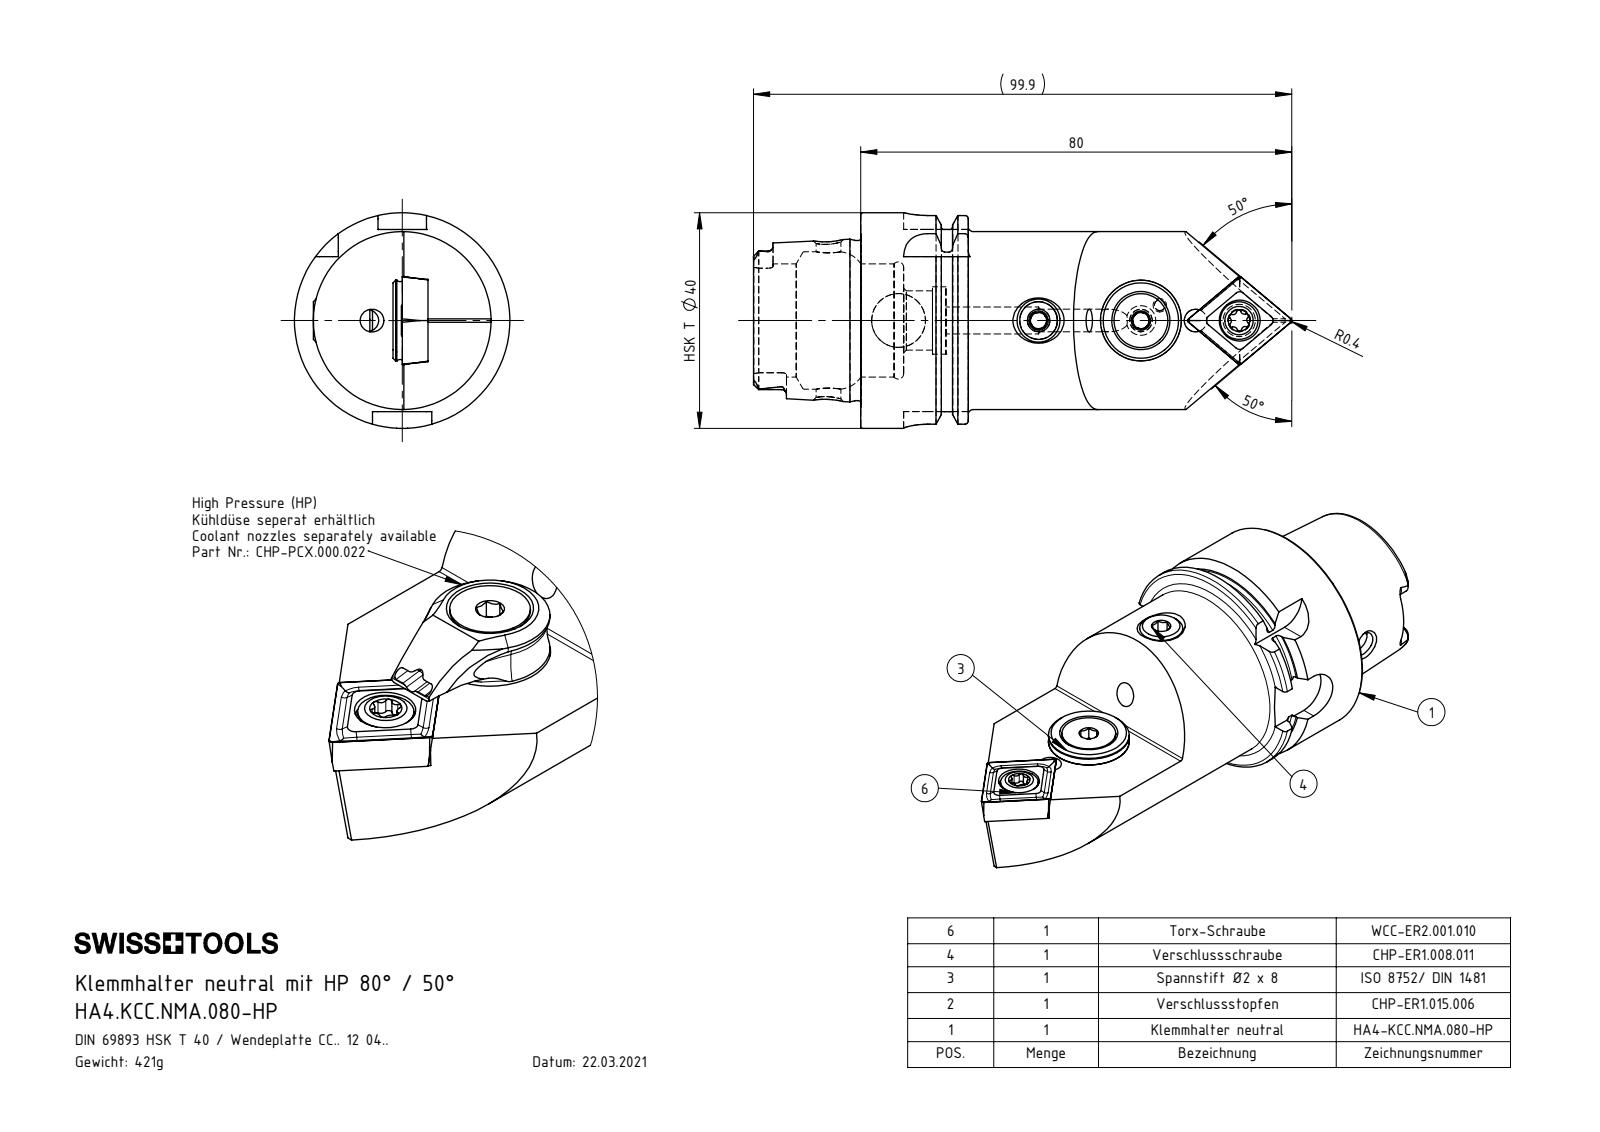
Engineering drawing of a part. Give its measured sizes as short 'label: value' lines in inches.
name: CHP-ER1.015.006; HA4-KCC.NMA.080-HP_A_Fertigbearbeitung; DIN 3771 - 13x1; CHP-ER1.015.006_A (+6 more)
written by: SolidWorks 2022 (AUTOMOTIVE_DESIGN)
unit: in
bodies: 8 solids, 396 faces (111 planar, 117 cylindrical, 168 other)
size: 3.933 × 1.575 × 1.575
volume: 3.297 in³; area: 27.84 in²
holes: 5× ⌀0.165, 1× ⌀0.047, 1× ⌀0.079, 1× ⌀0.098, 1× ⌀0.118, 1× ⌀0.181, 1× ⌀0.197, 1× ⌀0.205, 1× ⌀0.217, 1× ⌀0.276, 1× ⌀0.299, 1× ⌀0.394
bosses: 2× ⌀0.197, 1× ⌀1.575, 1× ⌀1.368, 1× ⌀1.299, 1× ⌀1.17, 1× ⌀0.591, 1× ⌀0.528, 1× ⌀0.394
rounds: 6× R0.015, 6× R0.027, 6× R0.035, 4× R0.177, 2× R0.072, 2× R0.074, 1× R0.02, 1× R0.083
face distances: 0.177, 0.313, 0.472, 0.785, 0.783, 1.096, 1.569, 0.642, 1.406, 0.622
hole spacings: 0.177, 0.591, 0.595, 0.718, 0.722, 0.748, 0.893, 1.024
